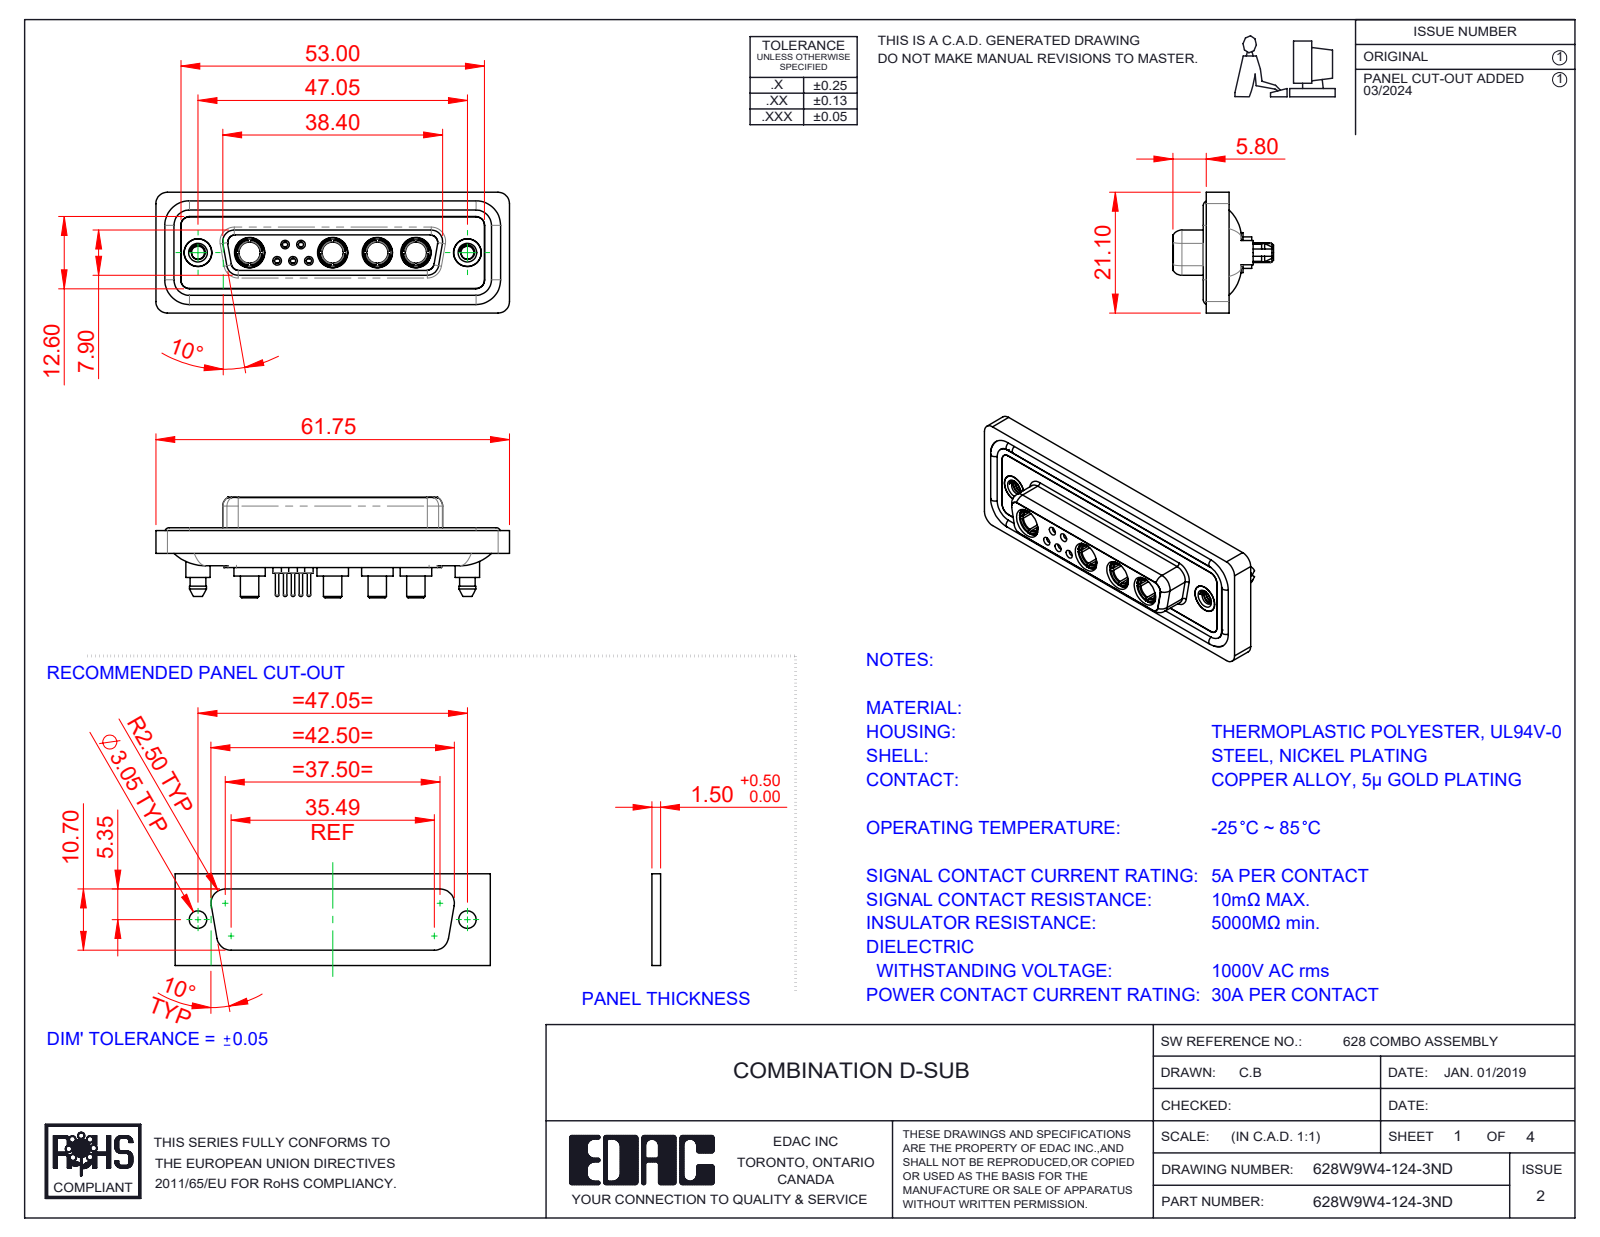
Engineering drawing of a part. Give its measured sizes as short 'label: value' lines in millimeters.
name: 628Combo Shell Rear_25 Contacts; 628W9W4-124-3ND; 628Combo Housing_9W4; 628Combo Threaded Boardlock_D (+5 more)
written by: SolidWorks 2023 (CONFIG_CONTROL_DESIGN)
unit: mm
bodies: 20 solids, 1023 faces (312 planar, 423 cylindrical, 288 other)
size: 61.75 × 21.1 × 17.55
volume: 8 387 mm³; area: 13 920 mm²
holes: 6× ⌀4.85, 5× ⌀0.9, 5× ⌀1.1, 5× ⌀1.5, 5× ⌀2, 4× ⌀3.7, 4× ⌀5.3, 3× ⌀1.6, 2× ⌀1.7, 2× ⌀2.26, 2× ⌀4, 2× ⌀4.05
bosses: 6× ⌀1.6, 5× ⌀2.2, 5× ⌀0.6, 4× ⌀5.5, 4× ⌀5.2, 4× ⌀4.96, 4× ⌀4.75, 4× ⌀3.75
rounds: 24× R1.5, 18× R2, 10× R1.6, 8× R1.35, 4× R0.25, 4× R0.5, 4× R0.6, 4× R0.65
face distances: 0.4, 1.8, 7.45, 5.65, 0.5, 7.05, 6.6, 1.6, 1.1, 2.9
hole spacings: 3.16, 2.77, 5.03, 2.76, 4.4, 5.02, 5.54, 5.73
